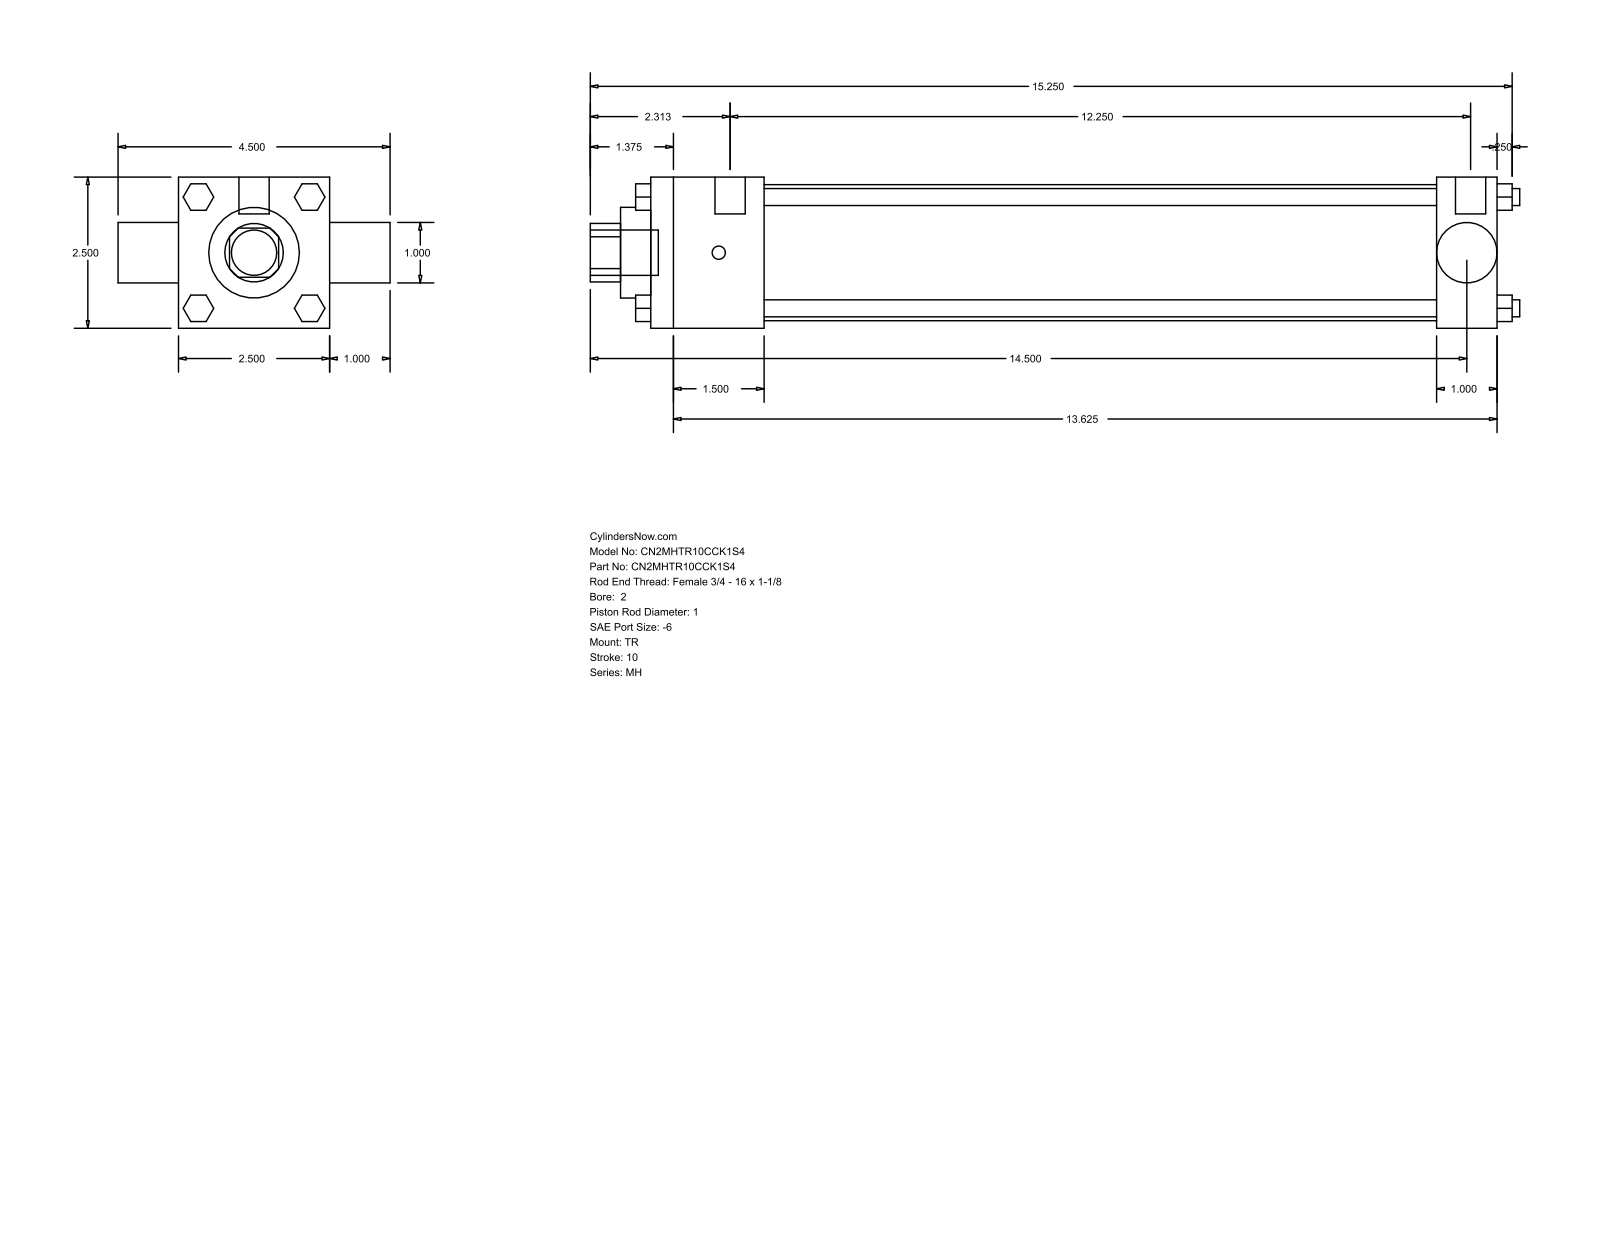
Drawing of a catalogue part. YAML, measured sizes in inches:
part_name: "MH_TR__0200_1"
step_written_by: "GSSL Pune (CONFIG_CONTROL_DESIGN)"
units: inches
bodies: {solids: 0, faces: 120, planar: 92, cylindrical: 28, other: 0}
overall_size: [15.375, 4.5, 2.5]
round_holes:
  - {diameter: 0.998, count: 1}
  - {diameter: 1, count: 1}
  - {diameter: 1.5, count: 1}
  - {diameter: 2.25, count: 1}
round_bosses_or_shafts:
  - {diameter: 0.281, count: 4}
  - {diameter: 0.219, count: 3}
  - {diameter: 0.5, count: 2}
  - {diameter: 0.75, count: 1}
partial_cylinders:
  - {radius: 0.484, count: 1}
face_to_face_distances: [2.5, 14, 1, 1.875, 13, 11.125, 12.125, 3.5, 14.5, 0.25]
